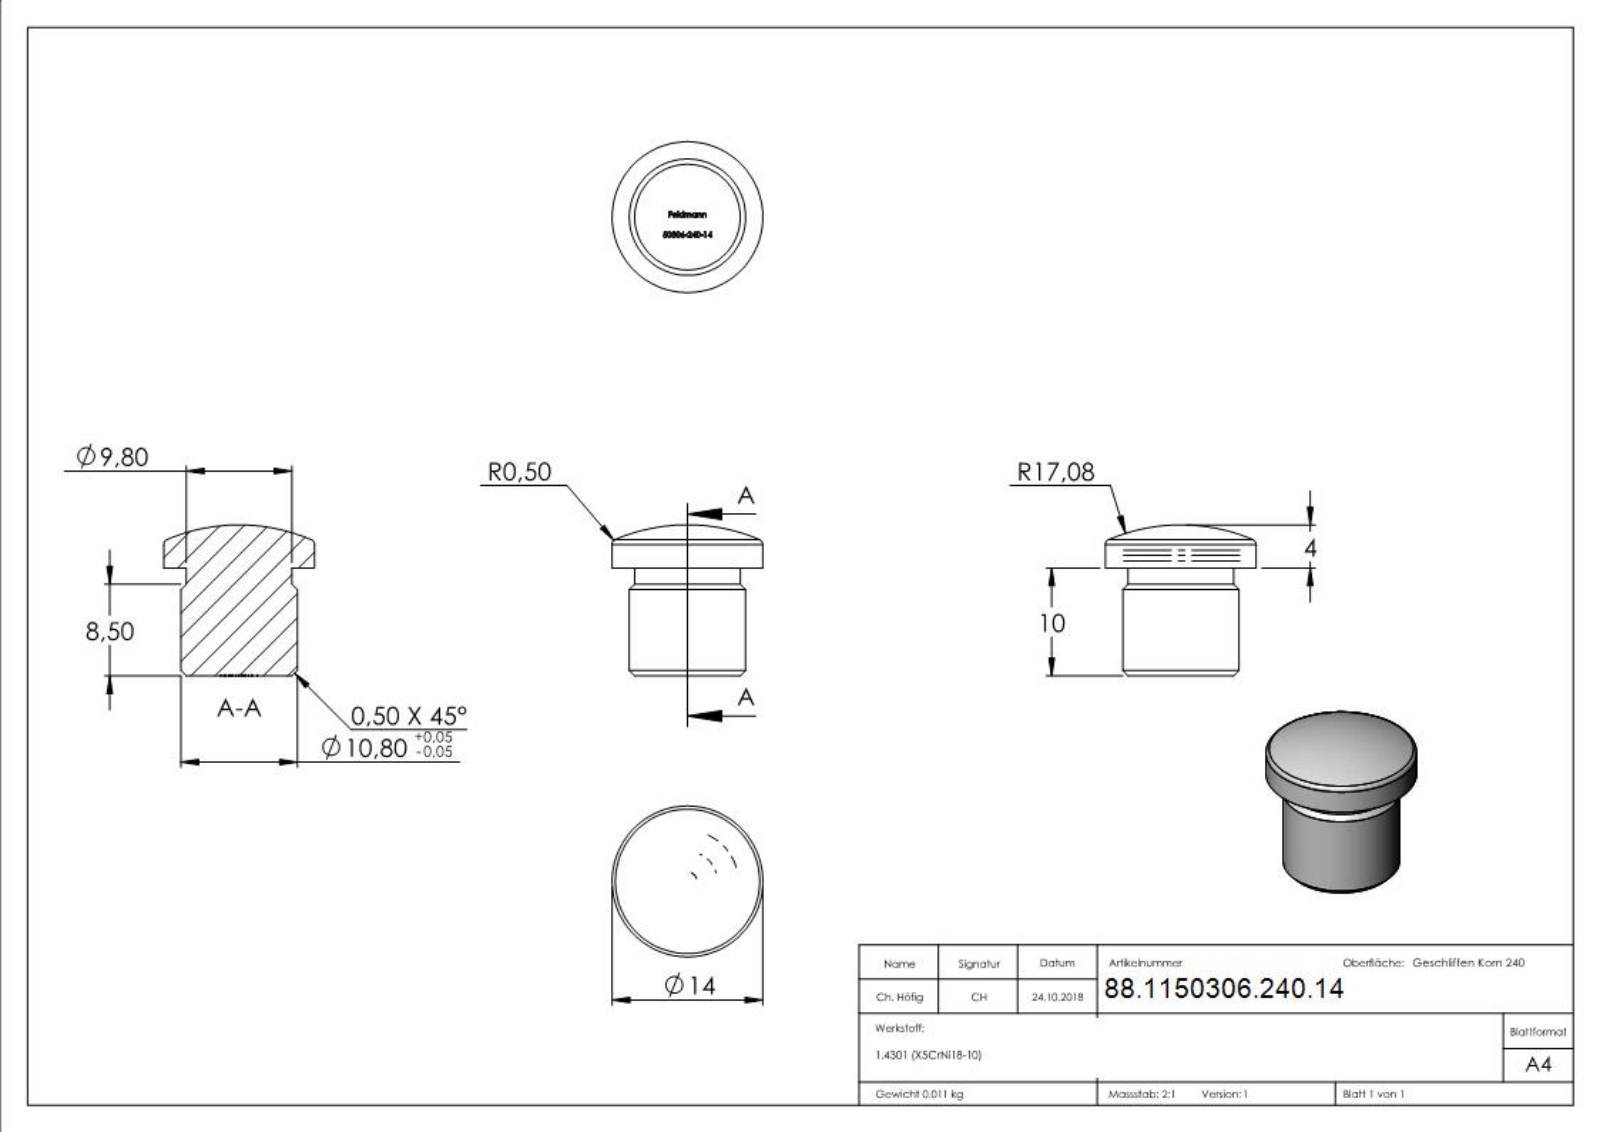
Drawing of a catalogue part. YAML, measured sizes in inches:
part_name: "50306-240-14"
step_written_by: "SolidWorks 2015 (CONFIG_CONTROL_DESIGN)"
units: inches
bodies: {solids: 1, faces: 269, planar: 143, cylindrical: 6, other: 120}
overall_size: [0.551, 0.551, 0.551]
volume: 0.085
surface_area: 1.2
round_bosses_or_shafts:
  - {diameter: 0.551, count: 1}
  - {diameter: 0.425, count: 1}
  - {diameter: 0.386, count: 1}
face_to_face_distances: [0.394, 0.39, 0.028, 0.026, 0.063, 0.074, 0.057, 0.081, 0.047, 0.065]
